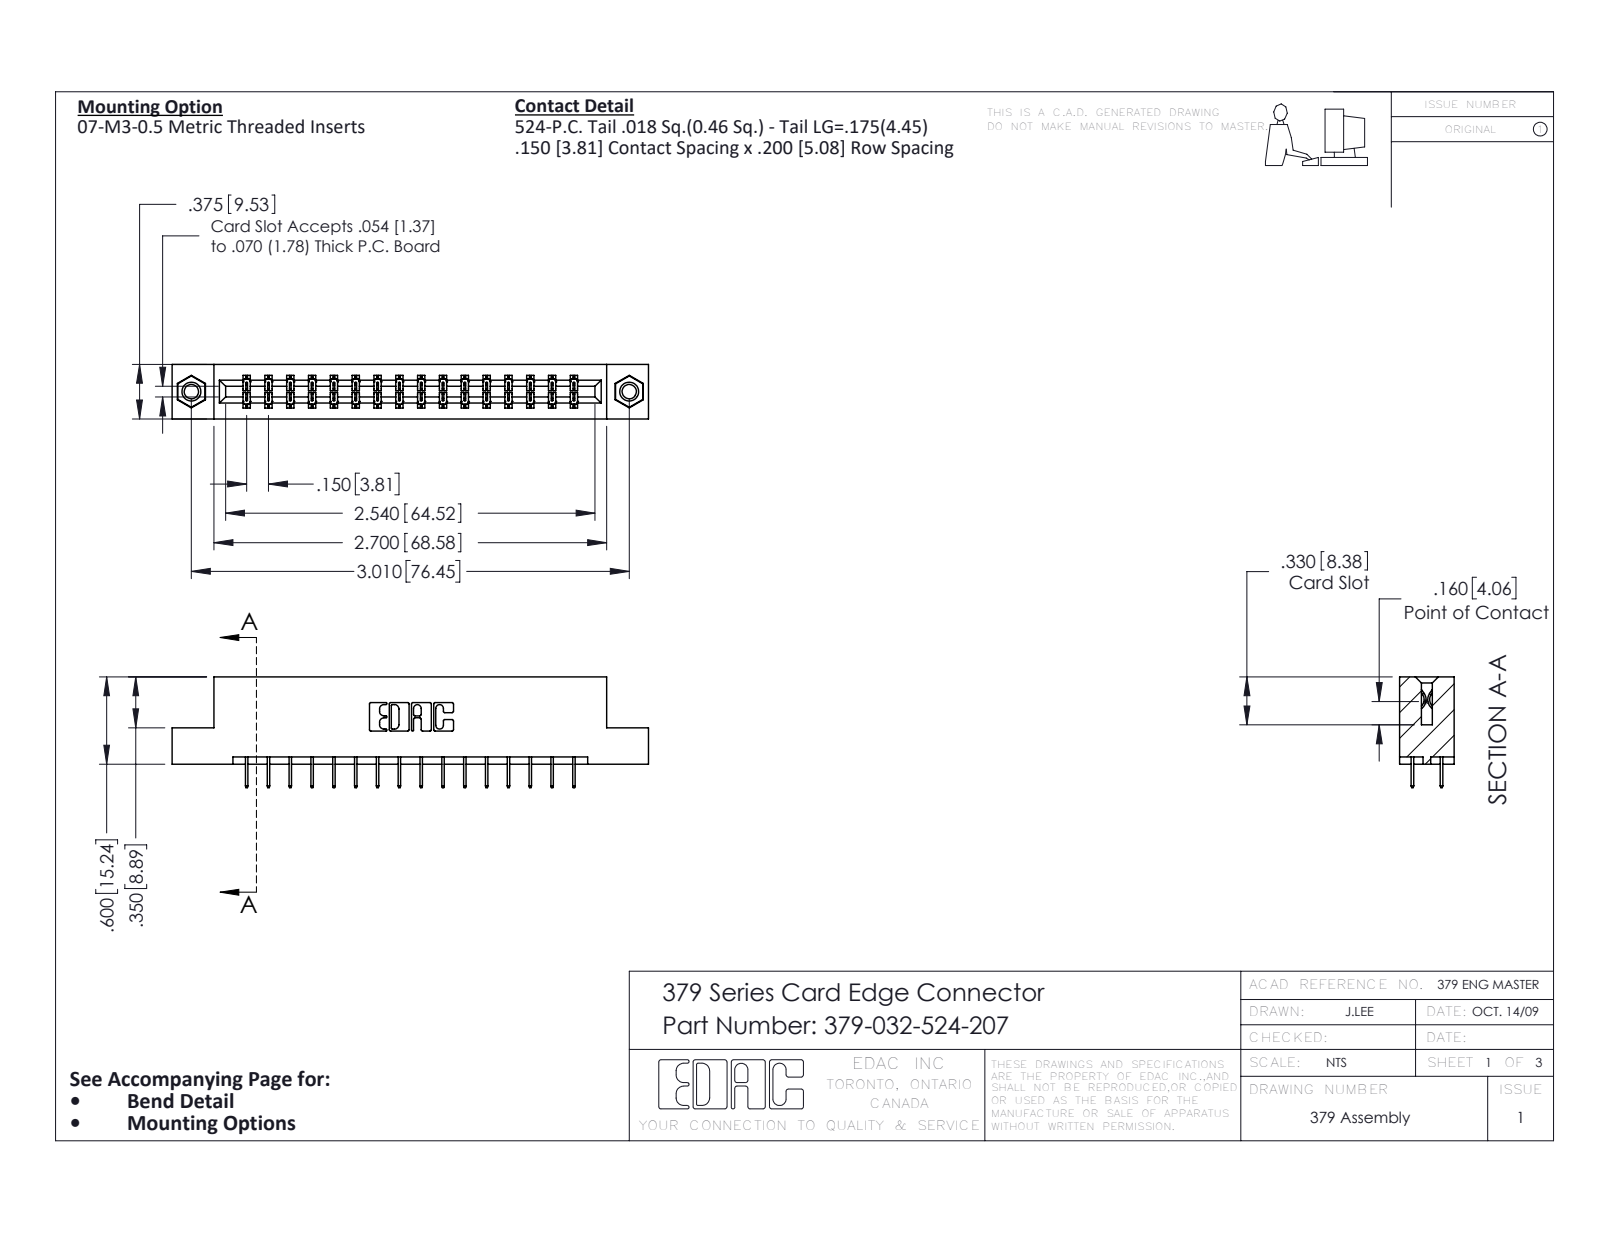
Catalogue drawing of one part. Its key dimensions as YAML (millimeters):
part_name: "379 Part_Flush - .156 Dia - TI; 345-292-001_345-293-124; 345-250-001_345-250-005-103; 379-032-524-207"
step_written_by: "SolidWorks 2020 (CONFIG_CONTROL_DESIGN)"
units: millimeters
bodies: {solids: 35, faces: 1966, planar: 1446, cylindrical: 504, other: 16}
overall_size: [83.2, 19.4, 9.5]
volume: 8470
surface_area: 9161
round_holes:
  - {diameter: 2.5, count: 2}
  - {diameter: 3.2, count: 2}
  - {diameter: 4, count: 2}
round_bosses_or_shafts:
  - {diameter: 3.9, count: 2}
partial_cylinders:
  - {radius: 0.2, count: 63}
  - {radius: 0.3, count: 22}
  - {radius: 0.2, count: 6}
  - {radius: 0.8, count: 6}
  - {radius: 0.7, count: 3}
  - {radius: 0.4, count: 2}
  - {radius: 0.6, count: 2}
  - {radius: 0.6, count: 2}
face_to_face_distances: [7.6, 9.5, 1.9, 5.1, 2.5, 3.8, 1.3, 15.2, 5.7, 14]
hole_center_spacings: [76.5]
